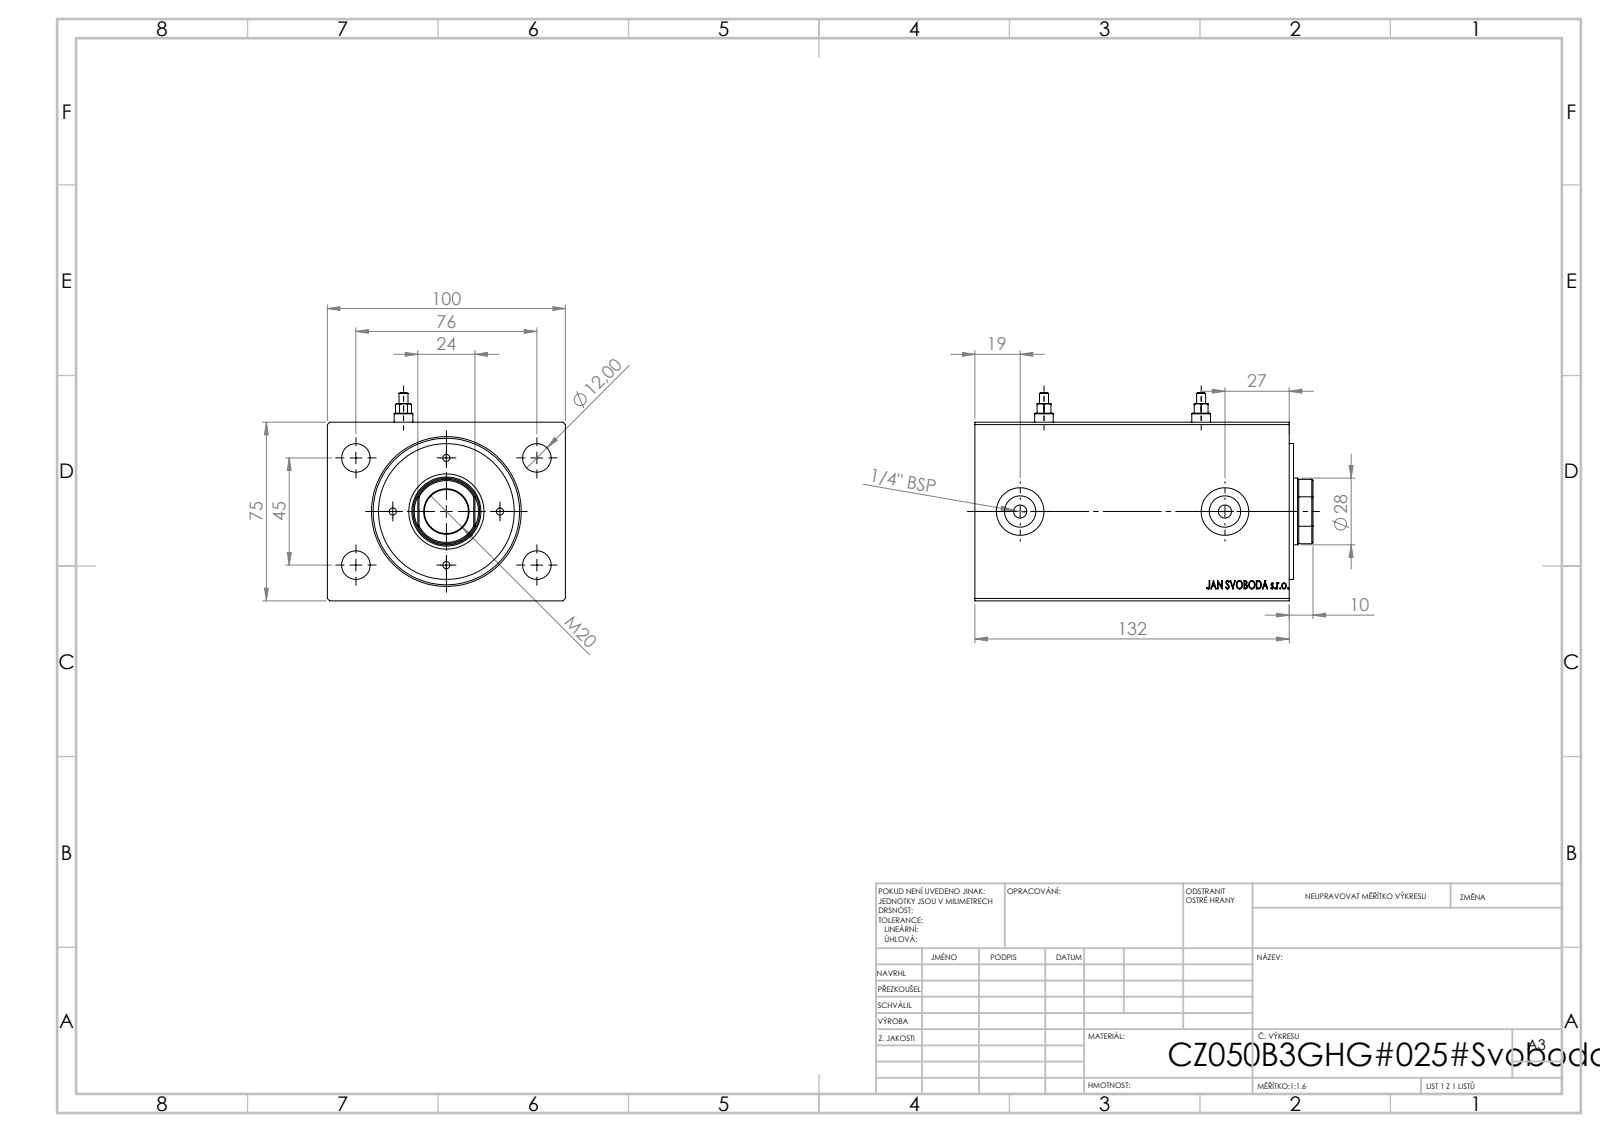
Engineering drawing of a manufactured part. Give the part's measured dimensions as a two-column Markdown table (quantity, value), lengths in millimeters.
| quantity | value |
| --- | --- |
| part name | Zatka_Cushioning3; V500CZ; V500CZ_B_VC |
| STEP written by | SolidWorks 2019 (CONFIG_CONTROL_DESIGN) |
| units | millimeters |
| bodies | 5 solids, 934 faces (424 planar, 74 cylindrical, 436 other) |
| overall size | 142 × 100 × 87.5 |
| volume | 925 424 mm³ |
| surface area | 118 310 mm² |
| round holes (diameter × count) | 3 × 4, 12 × 4, 1.8 × 2, 5.5 × 2, 8 × 2, 13.16 × 2, 20 × 2, 18.5 × 1, 28 × 1, 29 × 1, 36 × 1, 50 × 1 |
| round bosses / shafts (diameter × count) | 7.8 × 2, 3.8 × 2, 57 × 1 |
| partial cylindrical surfaces (radius × count) | 13.5 × 1 |
| main face-to-face distances | 75, 100, 132, 114.2, 17.8, 10, 1.8, 8.2, 106, 123.8 |
| hole center spacings | 22.5, 27.32, 31.82, 38, 44.16, 45, 58.9, 64.55 |
